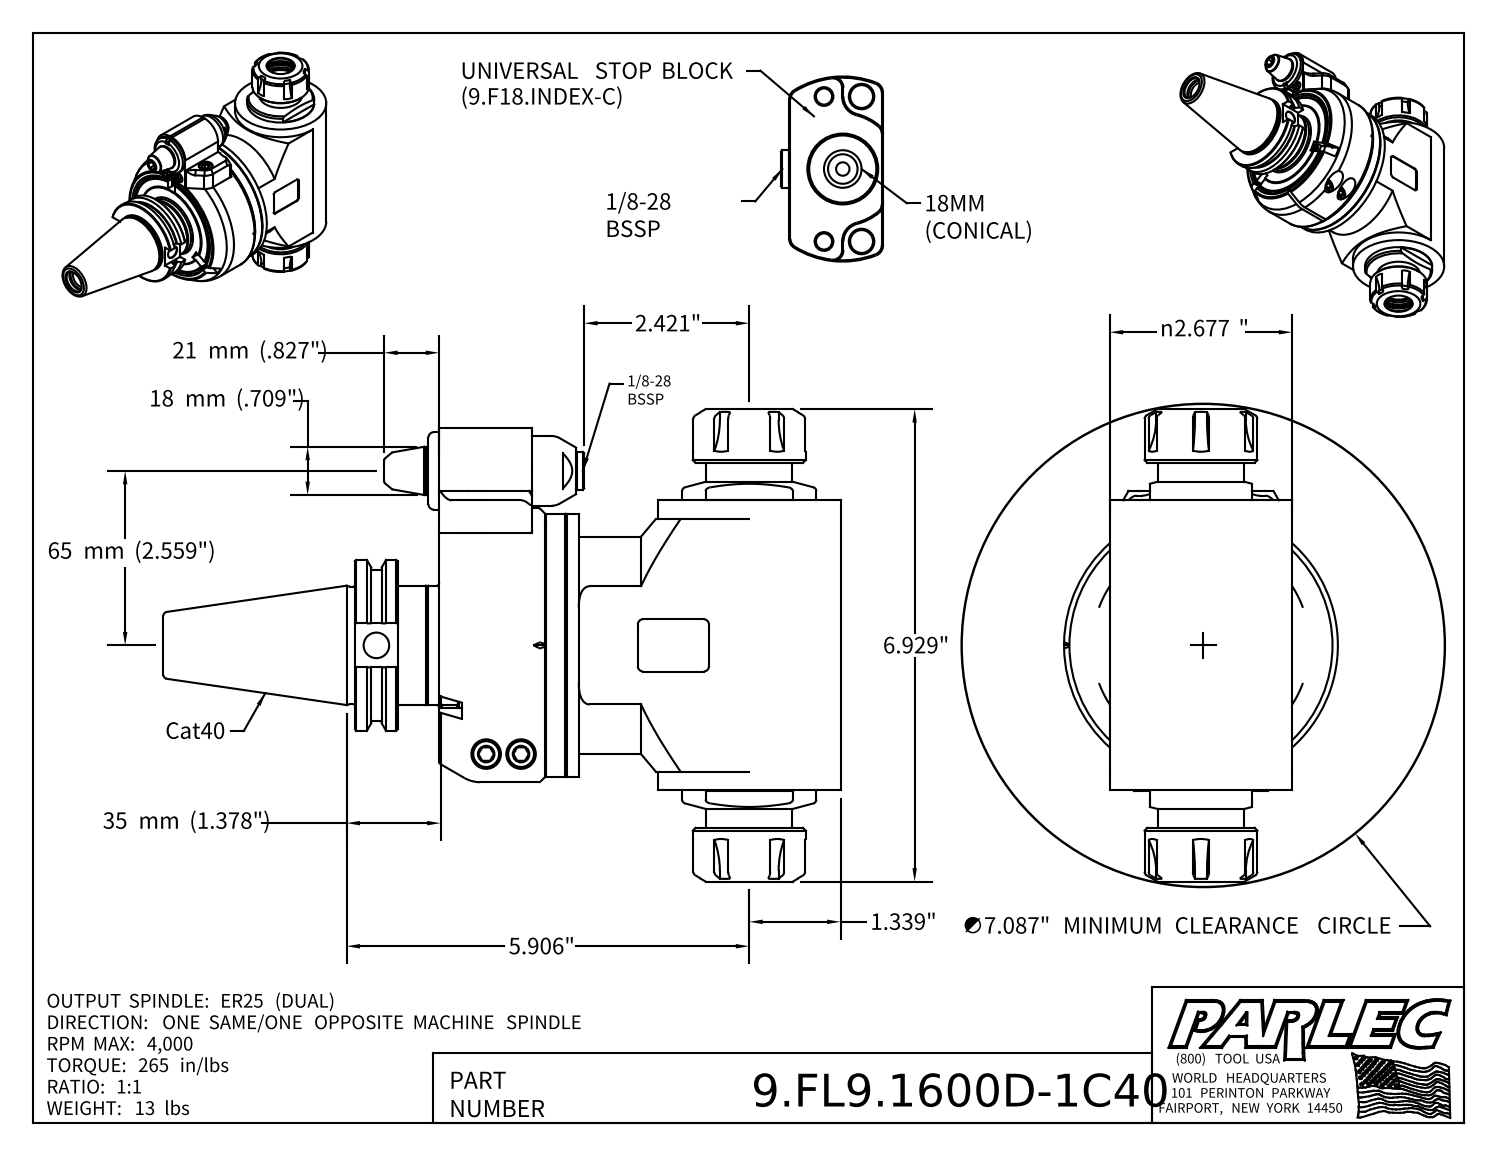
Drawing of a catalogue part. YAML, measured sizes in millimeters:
part_name: "9.FL9.1600D-1C40; 9_GA15C_446 (Type 1, Cat40, 65mm, conical); 9_FL9_16_2U0"
step_written_by: "Autodesk Inventor 2022 (AUTOMOTIVE_DESIGN)"
units: millimeters
bodies: {solids: 27, faces: 804, planar: 349, cylindrical: 218, other: 237}
overall_size: [252.2, 176, 102]
volume: 1082000
surface_area: 182300
round_holes:
  - {diameter: 5, count: 7}
  - {diameter: 4.2, count: 6}
  - {diameter: 3.2, count: 4}
  - {diameter: 3.3, count: 4}
  - {diameter: 6, count: 3}
  - {diameter: 8, count: 3}
  - {diameter: 2.6, count: 2}
  - {diameter: 6.5, count: 2}
  - {diameter: 6.8, count: 2}
  - {diameter: 10.4, count: 2}
  - {diameter: 11, count: 2}
  - {diameter: 12.5, count: 2}
round_bosses_or_shafts:
  - {diameter: 10, count: 5}
  - {diameter: 6, count: 4}
  - {diameter: 4, count: 4}
  - {diameter: 22, count: 2}
  - {diameter: 18, count: 2}
  - {diameter: 12, count: 2}
  - {diameter: 5, count: 2}
  - {diameter: 102, count: 1}
partial_cylinders:
  - {radius: 1, count: 14}
  - {radius: 25, count: 12}
  - {radius: 3, count: 6}
  - {radius: 2, count: 4}
  - {radius: 4, count: 4}
  - {radius: 0.5, count: 2}
  - {radius: 8, count: 2}
  - {radius: 14, count: 2}
face_to_face_distances: [7, 68, 0.5, 5, 39.5, 34, 32.5, 12, 12.5, 52]
hole_center_spacings: [8.3, 11.7, 7, 12, 12.8, 16.5, 18.8, 21.3]
